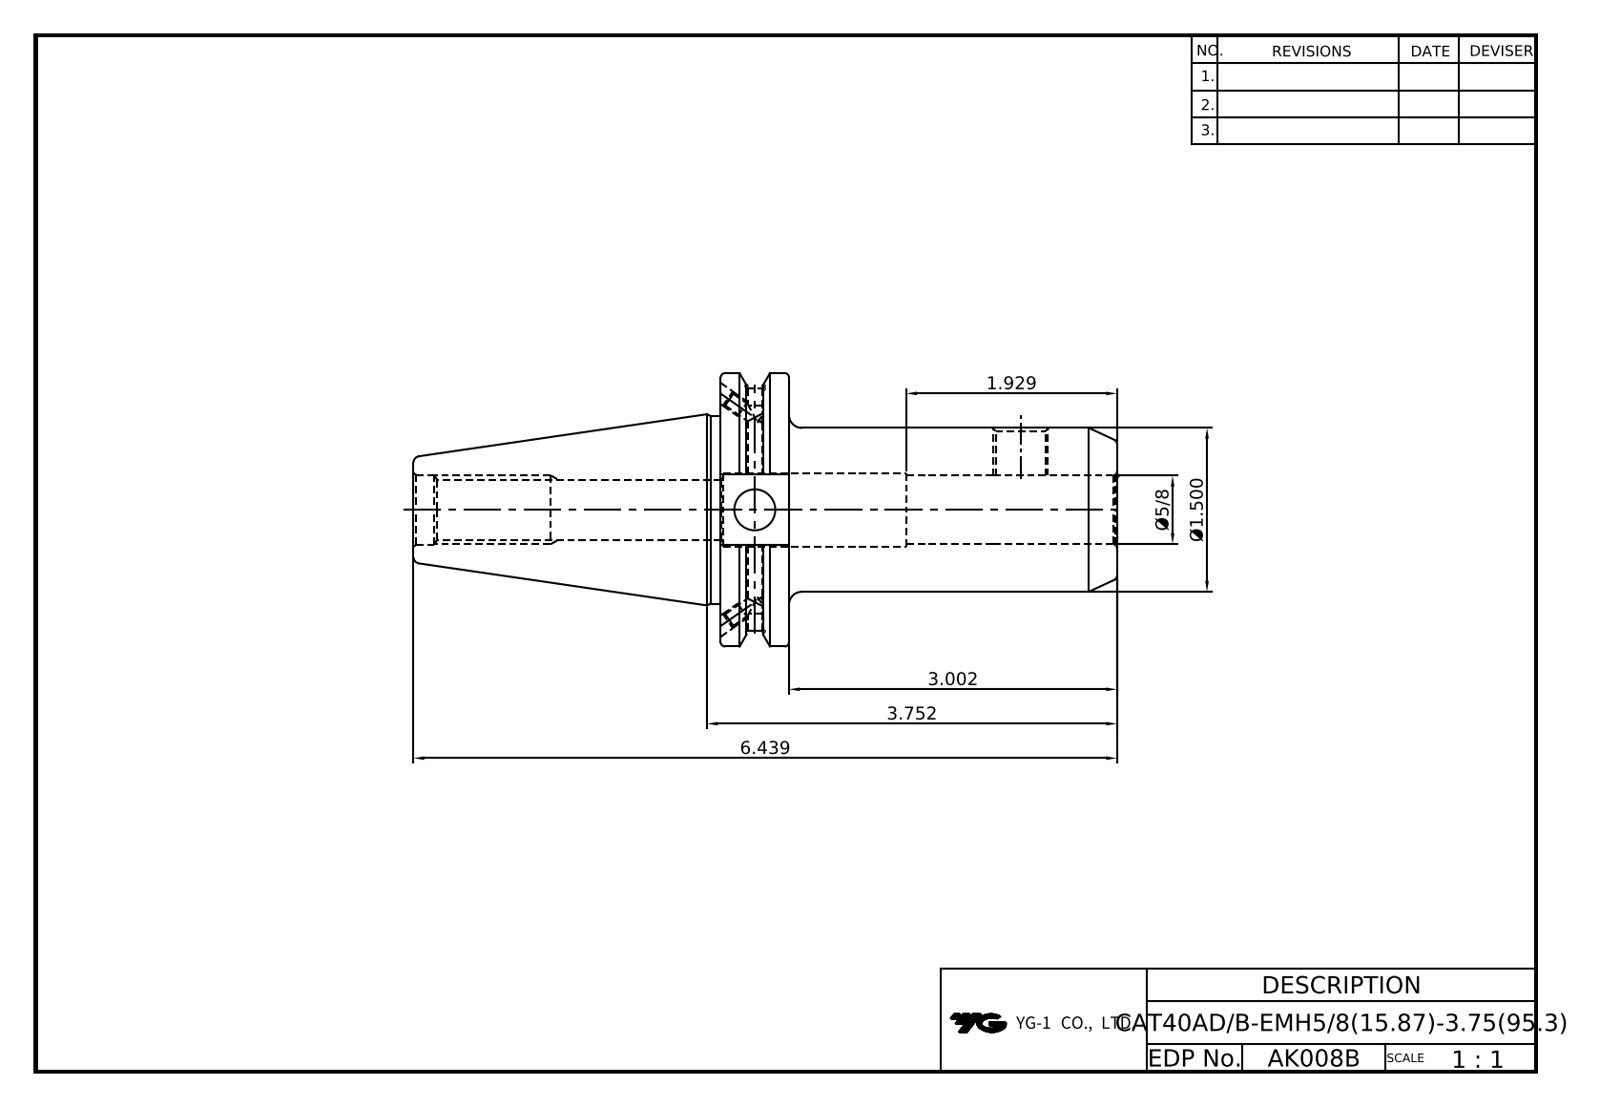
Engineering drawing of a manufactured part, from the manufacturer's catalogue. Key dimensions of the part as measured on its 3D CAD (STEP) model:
Part name (STEP PRODUCT): LO-CAT40ADB-EMH15.875-95.3
STEP written by: Autodesk Inventor 2020 (AUTOMOTIVE_DESIGN)
Units: millimetres
Bodies: 1 solid, 88 faces (38 planar, 28 cylindrical, 22 other)
Overall size (bounding box): 163.55 × 63.5 × 61.09
Volume: 168 148 mm³ · Surface area: 33 704 mm²
Round holes (diameter × count): ⌀3.24 ×4, ⌀4 ×2, ⌀4.2 ×2, ⌀9.53 ×1, ⌀11.33 ×1, ⌀13.39 ×1, ⌀15.87 ×1, ⌀16.3 ×1, ⌀16.47 ×1
Round bosses / shafts (diameter × count): ⌀63.5 ×1, ⌀43.6 ×1, ⌀38.1 ×1
Partial cylindrical surfaces — rounded edges, fillets, slot ends (radius × count): R28.15 ×1
Main face-to-face distances: 15.88, 92.13, 76.25, 47.6, 16.38, 71.42, 87.3, 163.55, 77.47, 6.05
